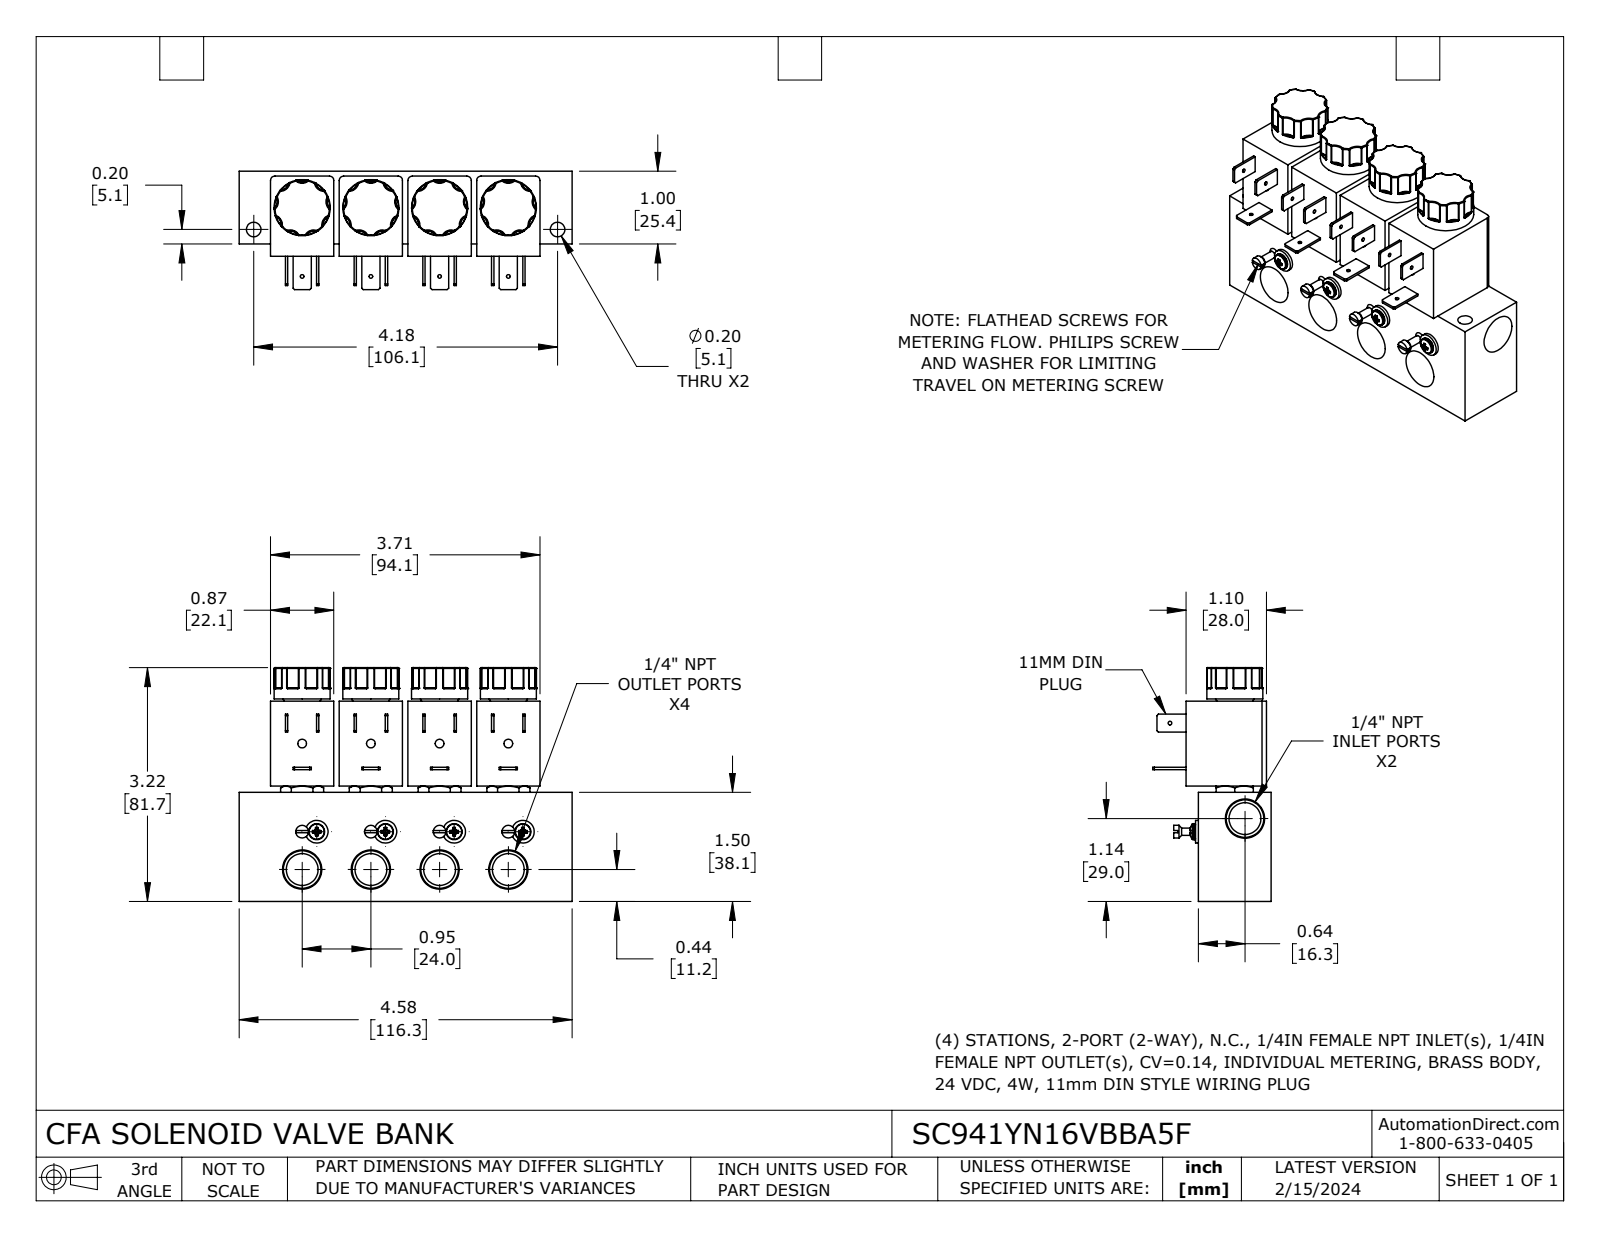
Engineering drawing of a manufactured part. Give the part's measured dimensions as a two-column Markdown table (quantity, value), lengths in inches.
| quantity | value |
| --- | --- |
| part name | SC941YN16VBBA5F |
| STEP written by | SolidWorks 2023 (CONFIG_CONTROL_DESIGN) |
| units | inches |
| bodies | 1 solid, 1098 faces (284 planar, 260 cylindrical, 554 other) |
| overall size | 4.578 × 3.215 × 1.627 |
| volume | 11.49 in³ |
| surface area | 68.21 in² |
| round holes (diameter × count) | 0.05 × 5, 0.438 × 5, 0.12 × 4, 0.2 × 2 |
| round bosses / shafts (diameter × count) | 0.77 × 4, 0.312 × 4, 0.219 × 4, 0.175 × 4, 0.1 × 4 |
| partial cylindrical surfaces (radius × count) | 0.01 × 72, 0.133 × 28, 0.06 × 8, 0.132 × 8 |
| main face-to-face distances | 1, 0.945, 1.169, 0.169, 1.89, 0.87, 1.815, 1.5, 0.065, 0.935 |
| hole center spacings | 0.945, 1.732, 1.973, 0.945, 1.89, 1.89, 2.835, 1.973 |
